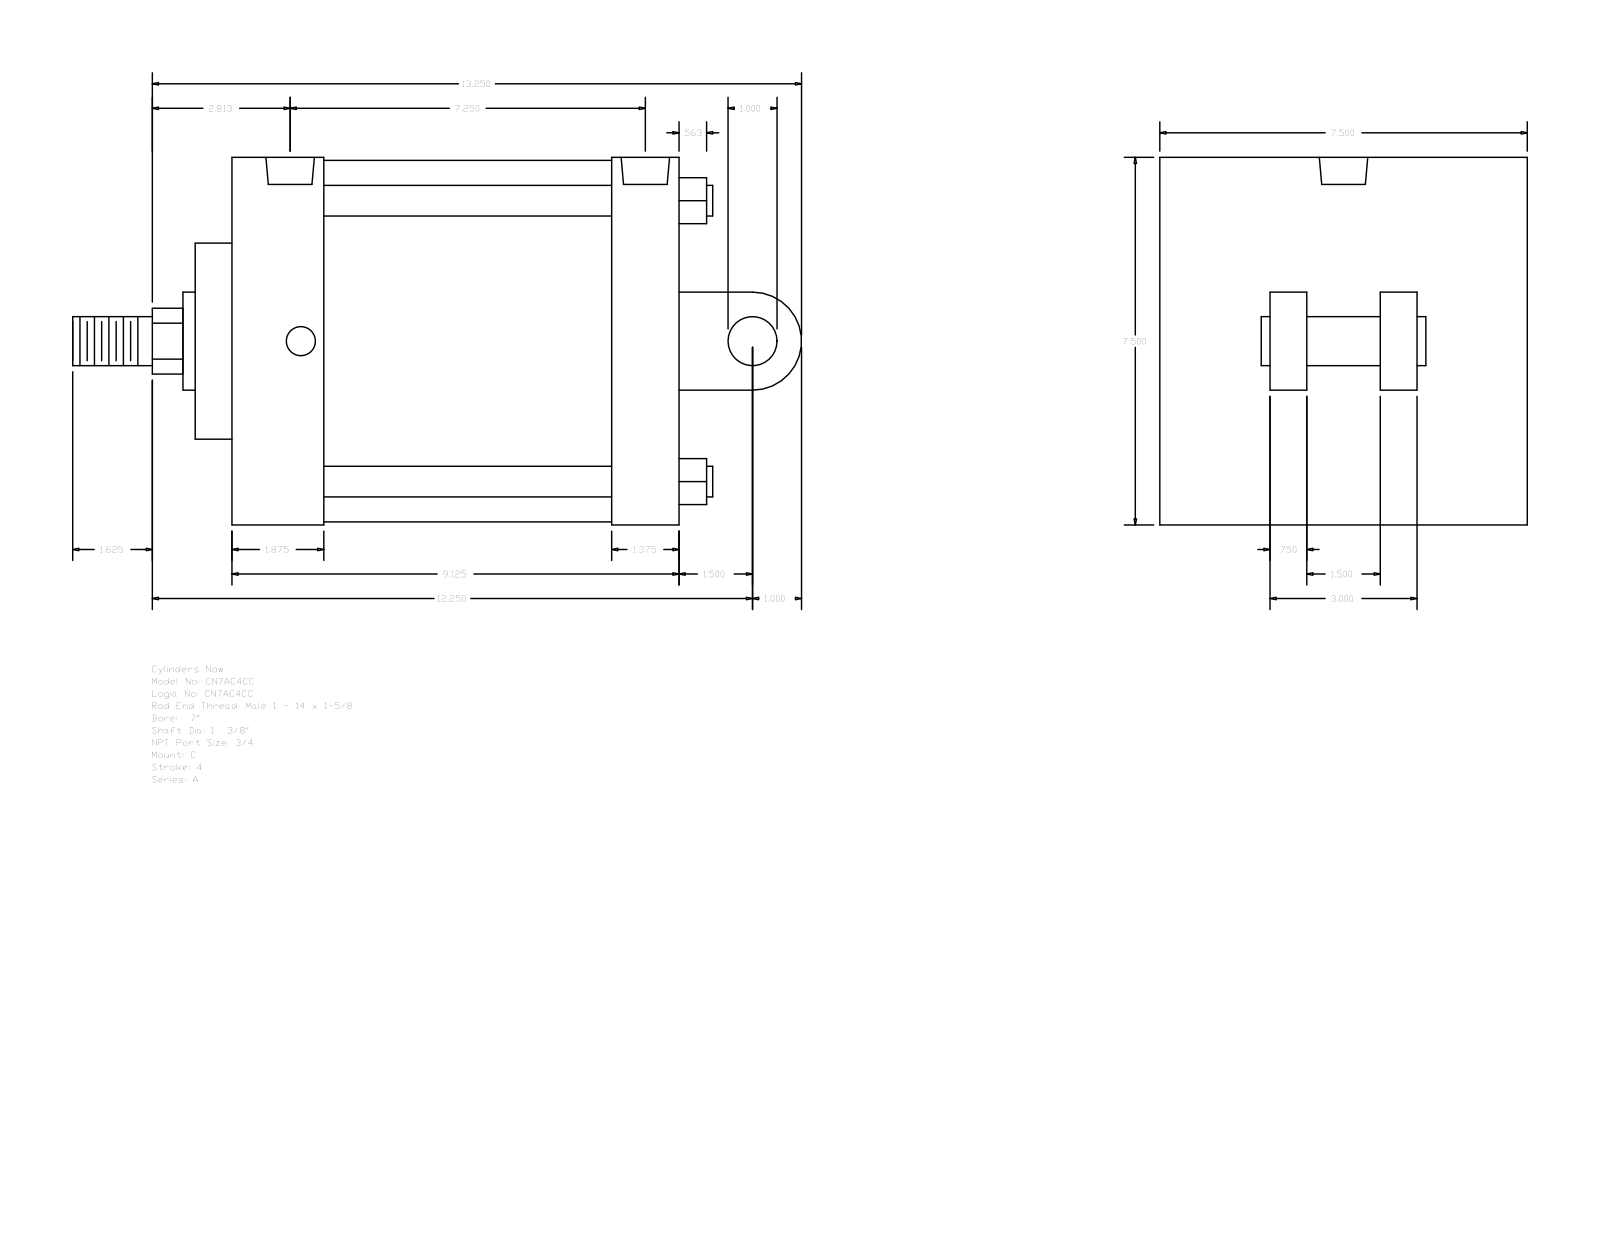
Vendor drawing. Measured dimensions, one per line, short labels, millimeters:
name: A_C__0700_1.375
written by: GSSL Pune (CONFIG_CONTROL_DESIGN)
unit: mm
bodies: 0 solids, 104 faces (75 planar, 29 cylindrical, 0 other)
size: 377.82 × 190.5 × 190.5
holes: 4× ⌀15.08, 2× ⌀25.12
bosses: 4× ⌀15.88, 2× ⌀25.4, 1× ⌀187.32, 1× ⌀50.8, 1× ⌀34.92
rounds: 1× R17.06, 1× R25.4
face distances: 190.5, 231.78, 76.2, 57.15, 19.04, 250.82, 66.67, 47.63, 184.15, 215.89
hole spacings: 5.56, 173.03, 178.59, 184.15
